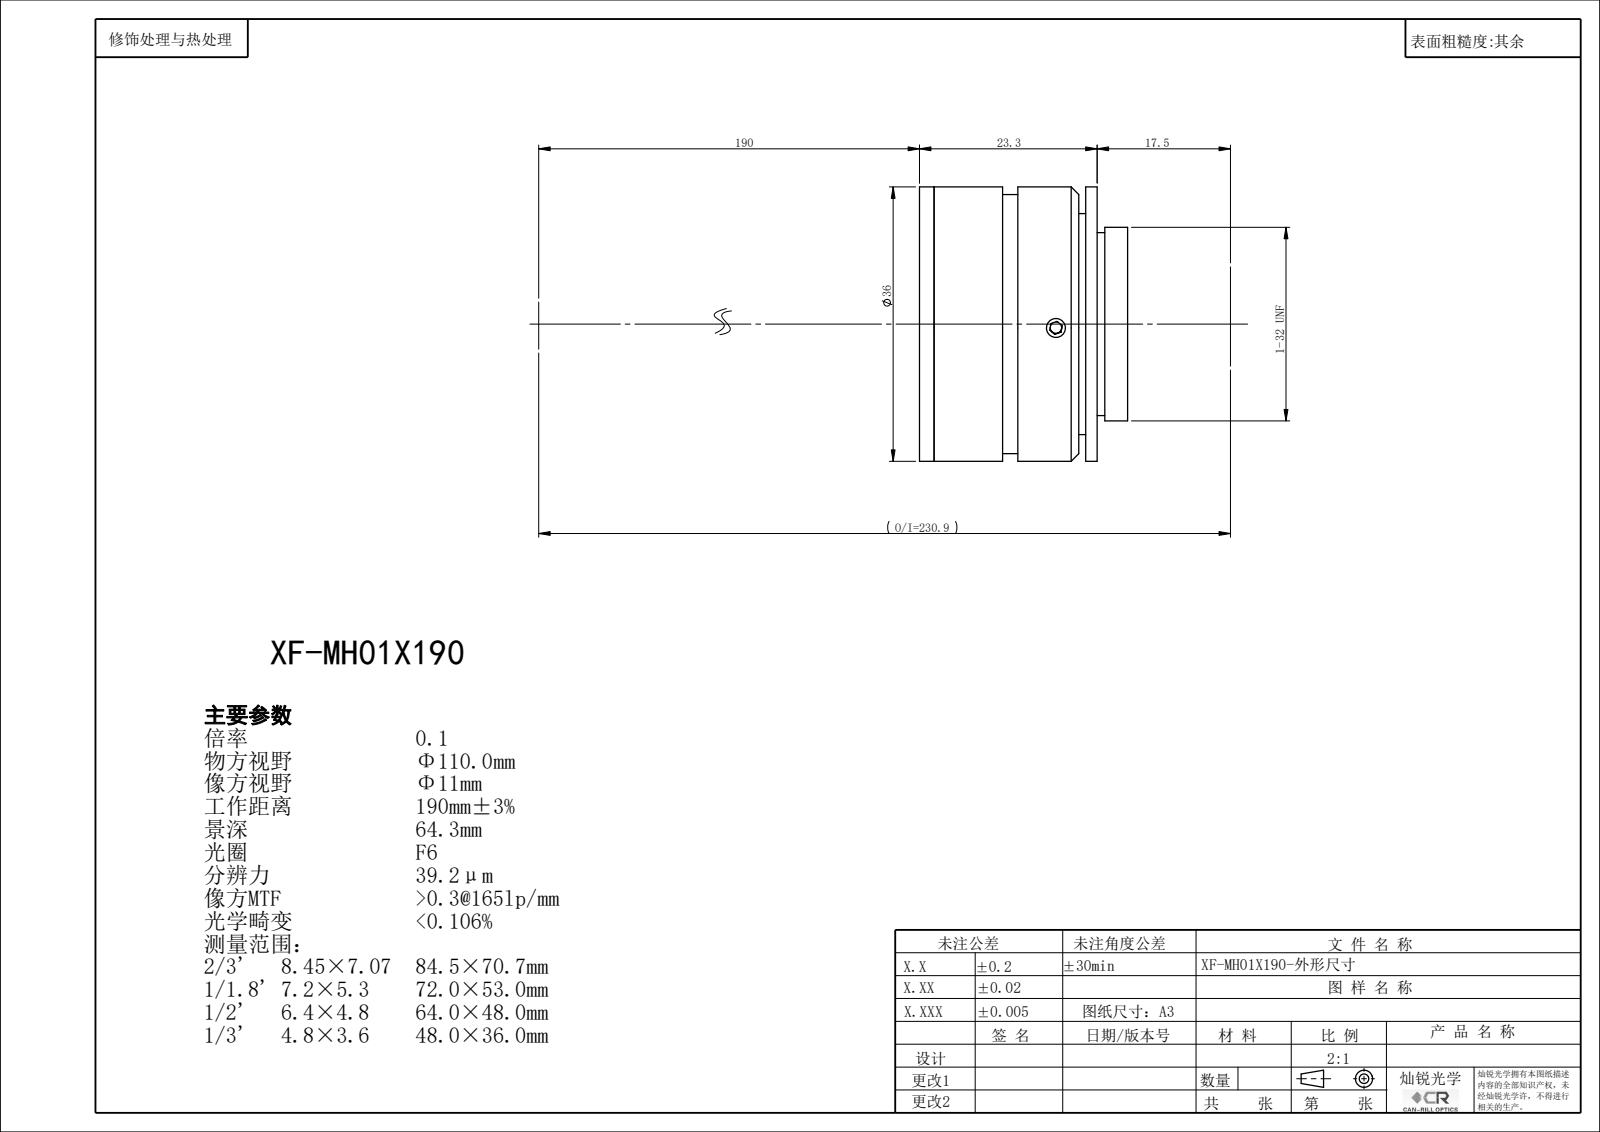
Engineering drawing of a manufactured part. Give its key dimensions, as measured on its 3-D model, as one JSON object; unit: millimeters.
{"part_name": "XF-MH01X190", "step_written_by": "SolidWorks 2022 (CONFIG_CONTROL_DESIGN)", "units": "millimeters", "bodies": {"solids": 0, "faces": 108, "planar": 50, "cylindrical": 48, "other": 10}, "overall_size": [36, 36, 27.32], "round_holes": [[2.5, 3], [7, 1], [8.4, 1], [10, 1], [12, 1], [14, 1], [16, 1], [18, 1], [20, 1], [21.5, 1], [22, 1], [24, 1]], "round_bosses_or_shafts": [[36, 1], [34, 1], [25.4, 1], [9, 1]], "face_to_face_distances": [1.91, 21.41, 23.32, 19.91, 2, 1, 1.5, 21.82, 0.91, 20.91]}
